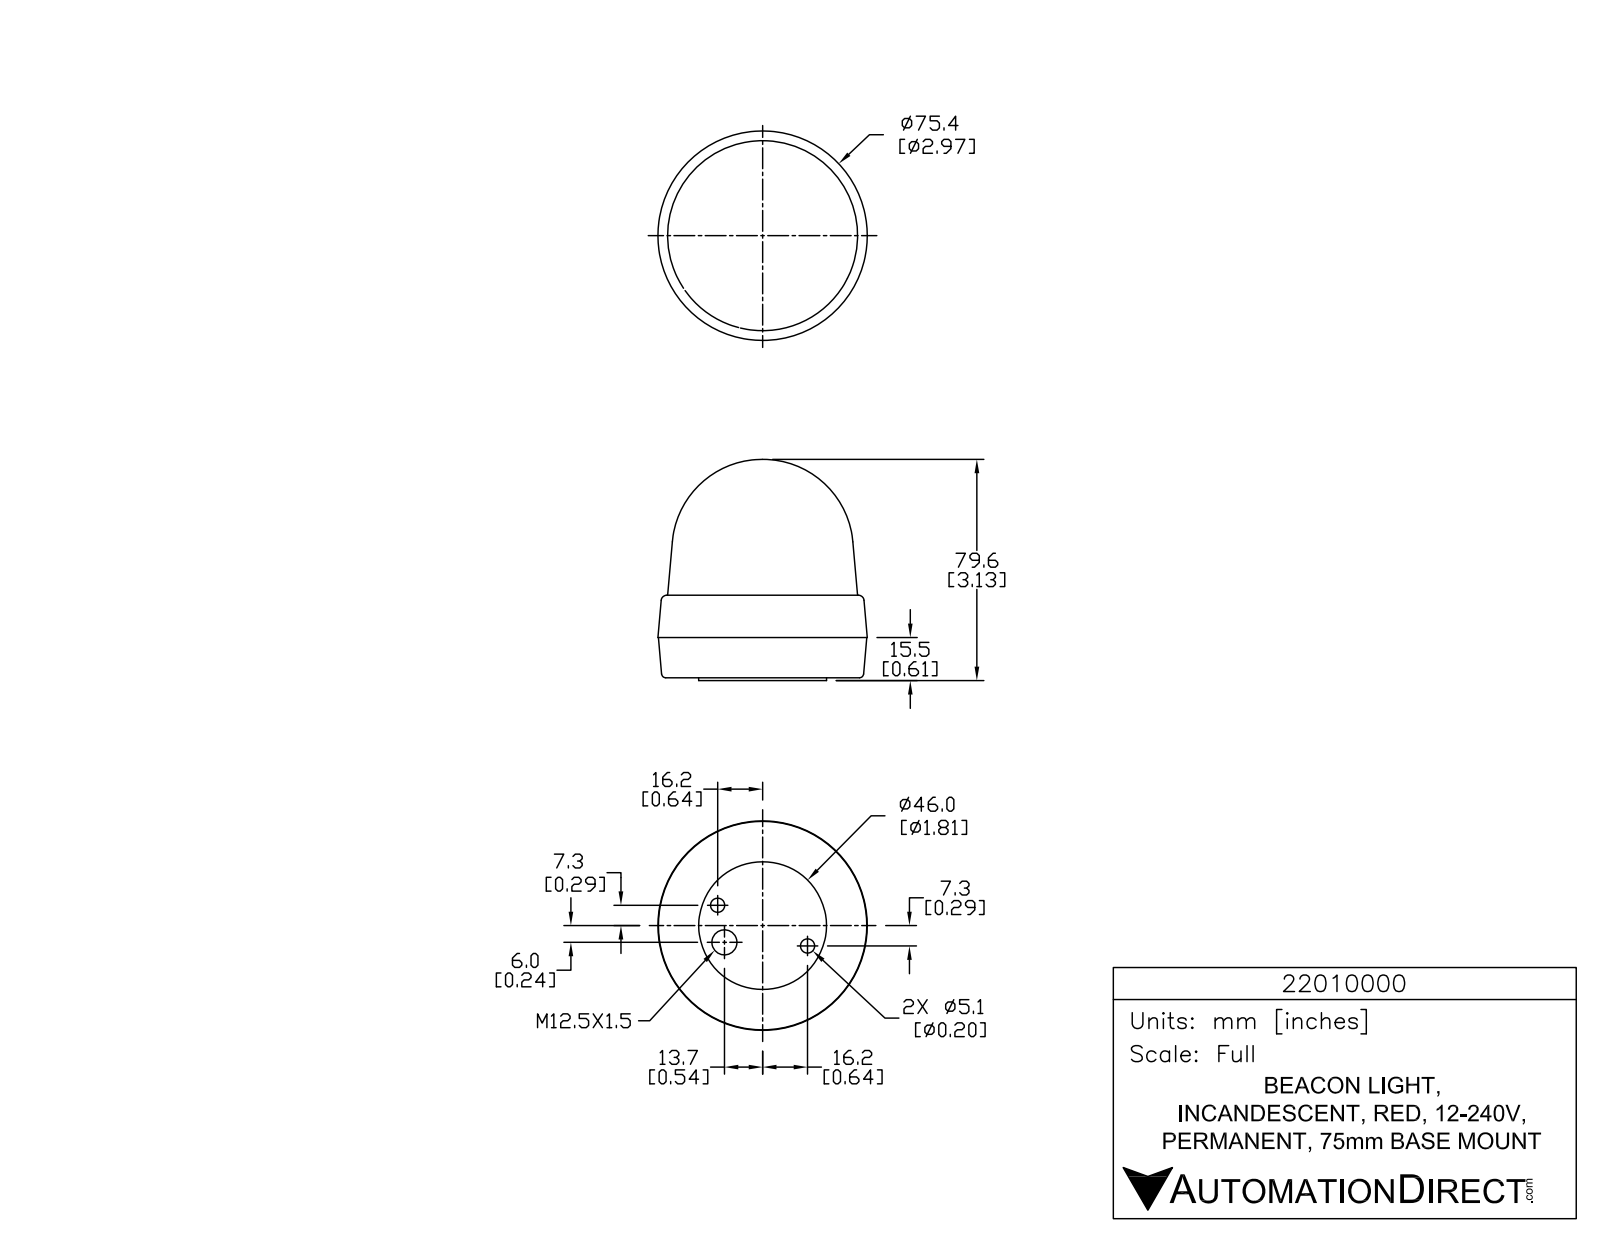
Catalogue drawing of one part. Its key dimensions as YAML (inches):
part_name: "22010000"
step_written_by: "SolidWorks 2015 (AUTOMOTIVE_DESIGN)"
units: inches
bodies: {solids: 1, faces: 773, planar: 526, cylindrical: 163, other: 84}
overall_size: [3.133, 2.967, 2.967]
volume: 15.79
surface_area: 33.7
round_holes:
  - {diameter: 0.059, count: 3}
  - {diameter: 0.201, count: 2}
  - {diameter: 0.354, count: 1}
round_bosses_or_shafts:
  - {diameter: 0.339, count: 3}
  - {diameter: 0.084, count: 3}
  - {diameter: 1.811, count: 1}
partial_cylinders:
  - {radius: 0.005, count: 9}
  - {radius: 0.005, count: 6}
  - {radius: 0.012, count: 6}
  - {radius: 0.012, count: 6}
  - {radius: 0.012, count: 6}
  - {radius: 0.196, count: 6}
  - {radius: 0.005, count: 3}
  - {radius: 0.005, count: 3}
face_to_face_distances: [0.039, 1.209, 1.17, 0.61, 0.571, 0.599, 1.566, 1.527, 0.956, 0.357]
hole_center_spacings: [0.534, 1.179, 1.398]
